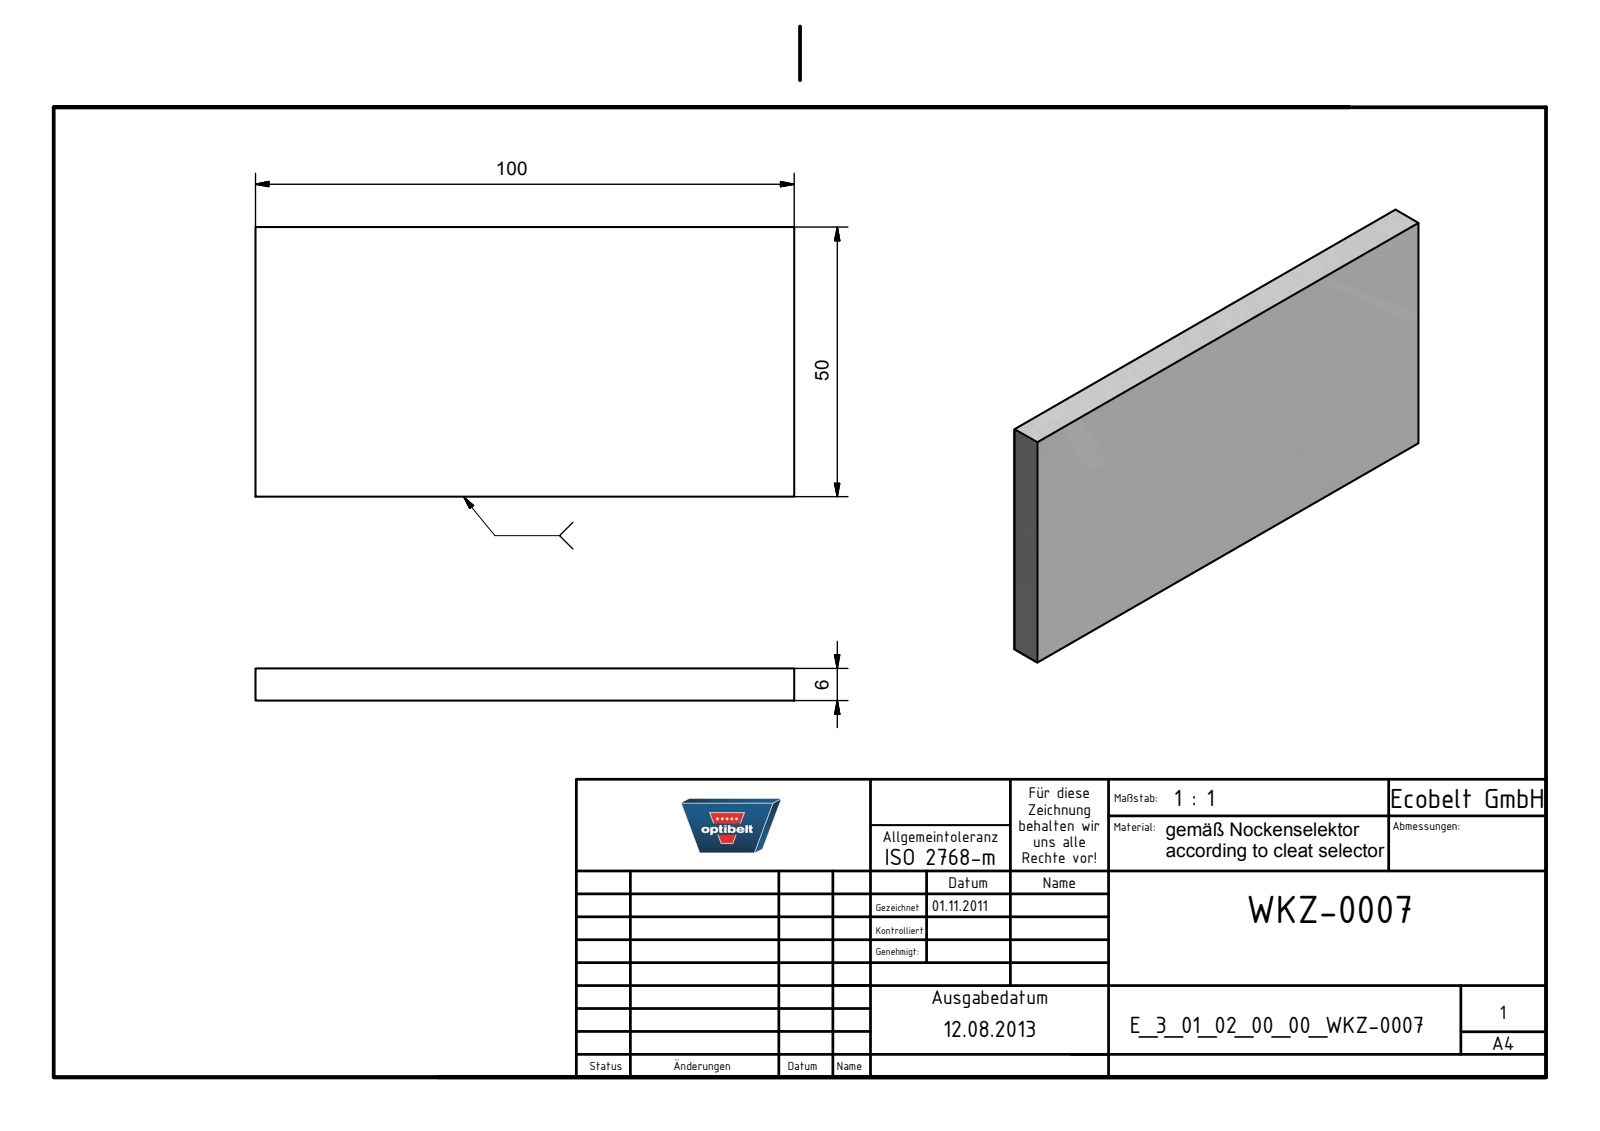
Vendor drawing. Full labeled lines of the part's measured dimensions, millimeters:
Part name (STEP PRODUCT): E_3_01_02_00_00_WKZ-0007
STEP written by: Autodesk Inventor 2021 (AUTOMOTIVE_DESIGN)
Units: millimetres
Bodies: 1 solid, 6 faces (6 planar, 0 cylindrical, 0 other)
Overall size (bounding box): 100 × 50 × 6
Volume: 30 000 mm³ · Surface area: 11 800 mm²
Main face-to-face distances: 6, 50, 100
